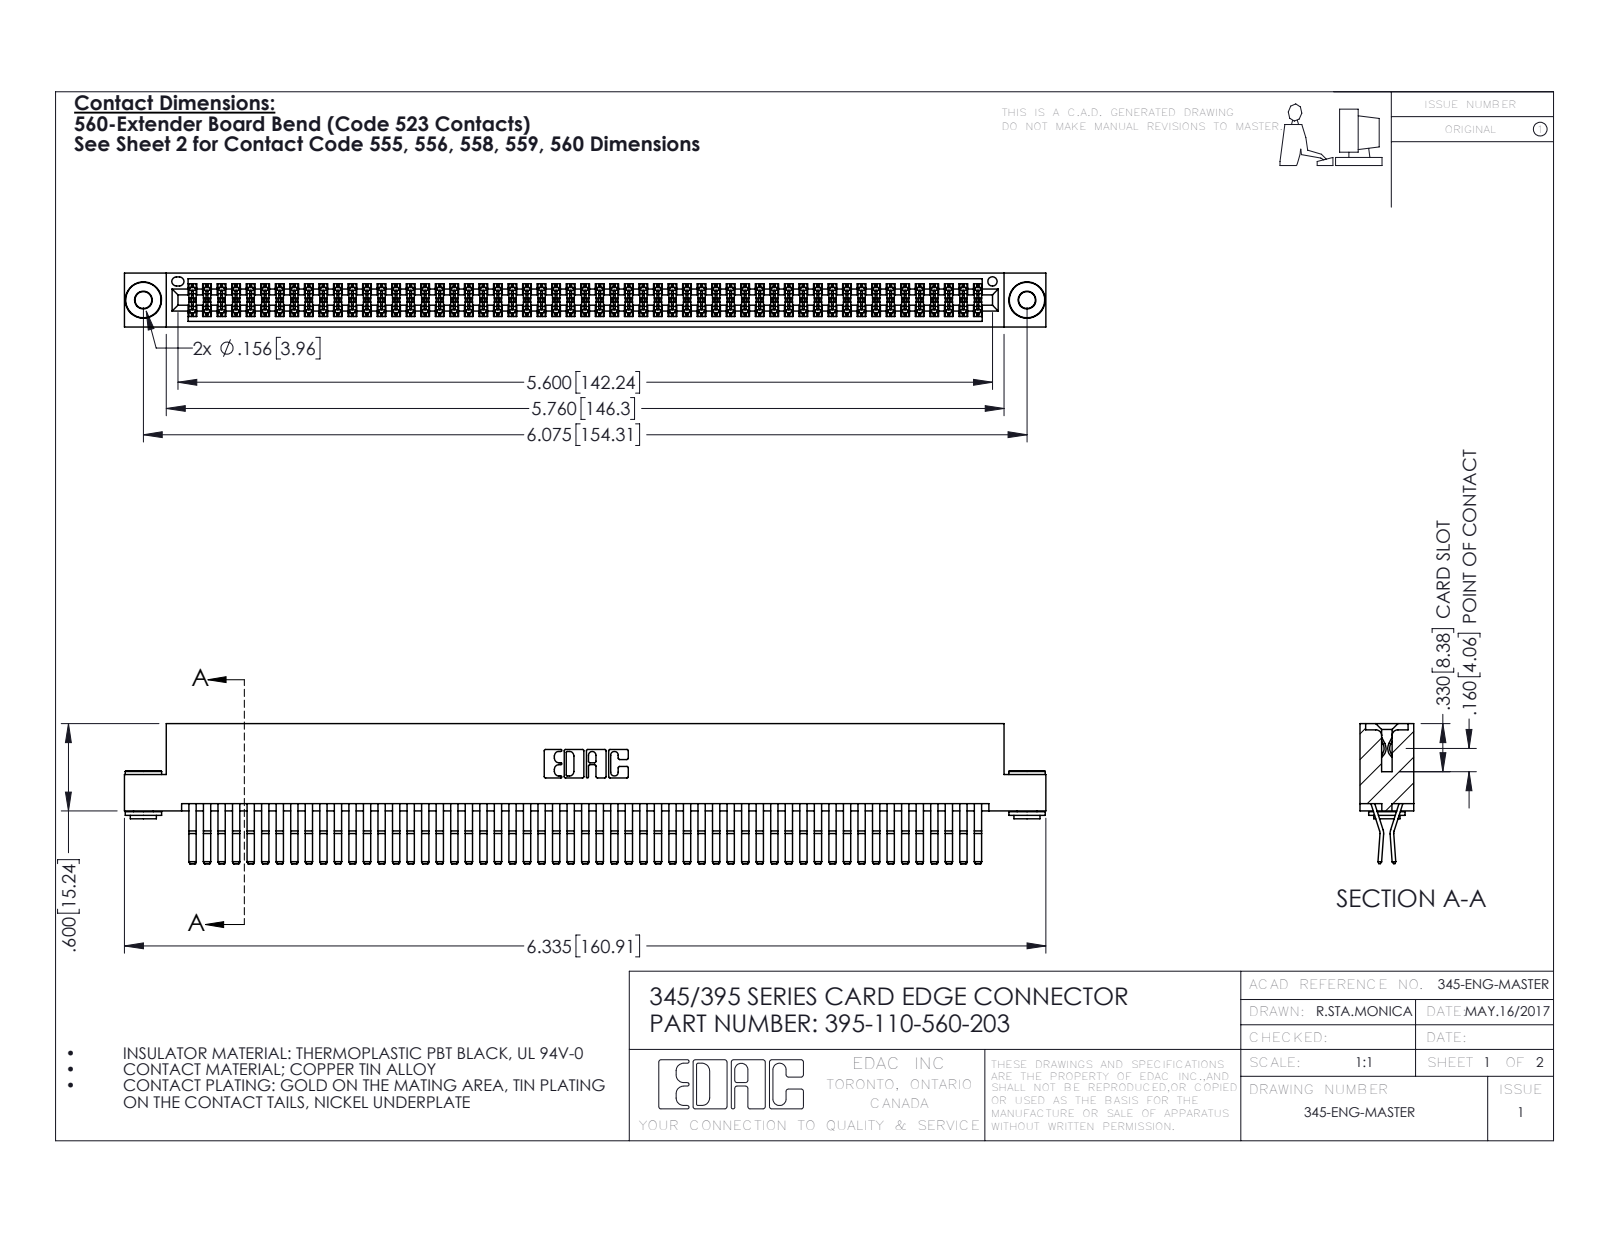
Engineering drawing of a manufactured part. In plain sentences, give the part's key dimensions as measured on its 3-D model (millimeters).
The part is named "345-250-002_345-250-002-102; 395-110-560-203; 345-292-001_560 Tail; 345 Part_Flush Mounting Lugs - 0.156 Dia-TH". Its 3-D file was written by "SolidWorks 2016 (CONFIG_CONTROL_DESIGN)". It is 113 solids with 5884 faces: 3720 planar, 2156 cylindrical and 8 other. Overall it measures 160.9 by 24.4 by 9.4 millimeters. Its volume is 16 490 cubic millimeters and its surface area 26 690 square millimeters. Round holes: 2 of diameter 2.9, 2 of diameter 4, 1 of diameter 1.6. Round bosses or shafts: 2 of diameter 6.4, 2 of diameter 4.6, 2 of diameter 3.5. Partial cylindrical surfaces (rounded edges, fillets, slot ends): 165 of radius 0.2, 22 of radius 0.3, 6 of radius 0.2, 6 of radius 0.8, 3 of radius 0.7, 2 of radius 0.3, 2 of radius 0.4, 2 of radius 0.5. The main face-to-face distances are 0.6, 1.8, 7.6, 9.4, 5.1, 2.5, 6.9, 5.7, 4.4, 3.8. The hole center spacings are 6.9, 148.3, 154.3.
